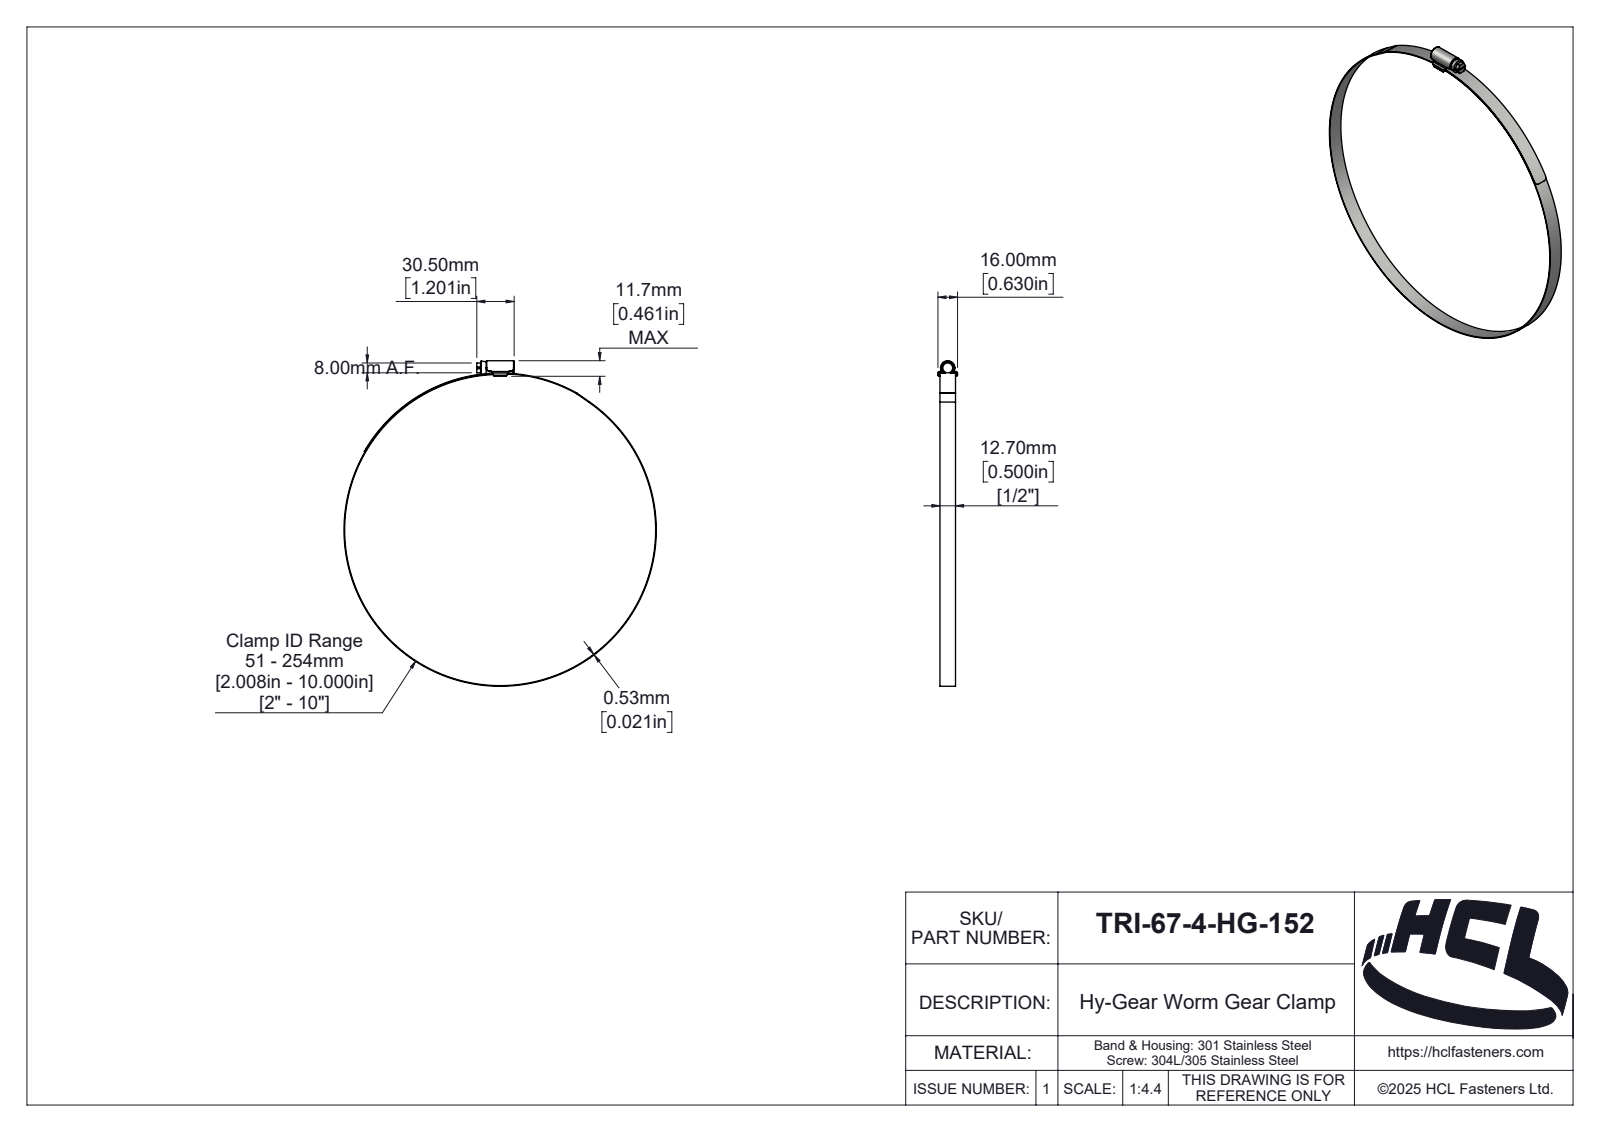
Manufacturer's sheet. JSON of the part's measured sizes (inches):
{"part_name": "TRI-67-4-HG", "step_written_by": "SolidWorks 2025 (CONFIG_CONTROL_DESIGN)", "units": "inches", "bodies": {"solids": 3, "faces": 189, "planar": 39, "cylindrical": 89, "other": 61}, "overall_size": [10.462, 10.042, 0.63], "volume_in3": 0.566, "surface_area_in2": 42.8, "round_holes": [[10, 1]], "round_bosses_or_shafts": [[10.042, 1], [0.394, 1]], "partial_cylinders_radius": [[0.02, 6], [0.118, 4], [0.004, 2], [0.035, 2], [0.047, 2], [0.018, 1], [0.074, 1], [0.079, 1]], "face_to_face_distances": [0.5, 0.031, 0.021, 0.122, 0.091, 0.154, 1.201, 0.065, 0.565, 0.598]}
